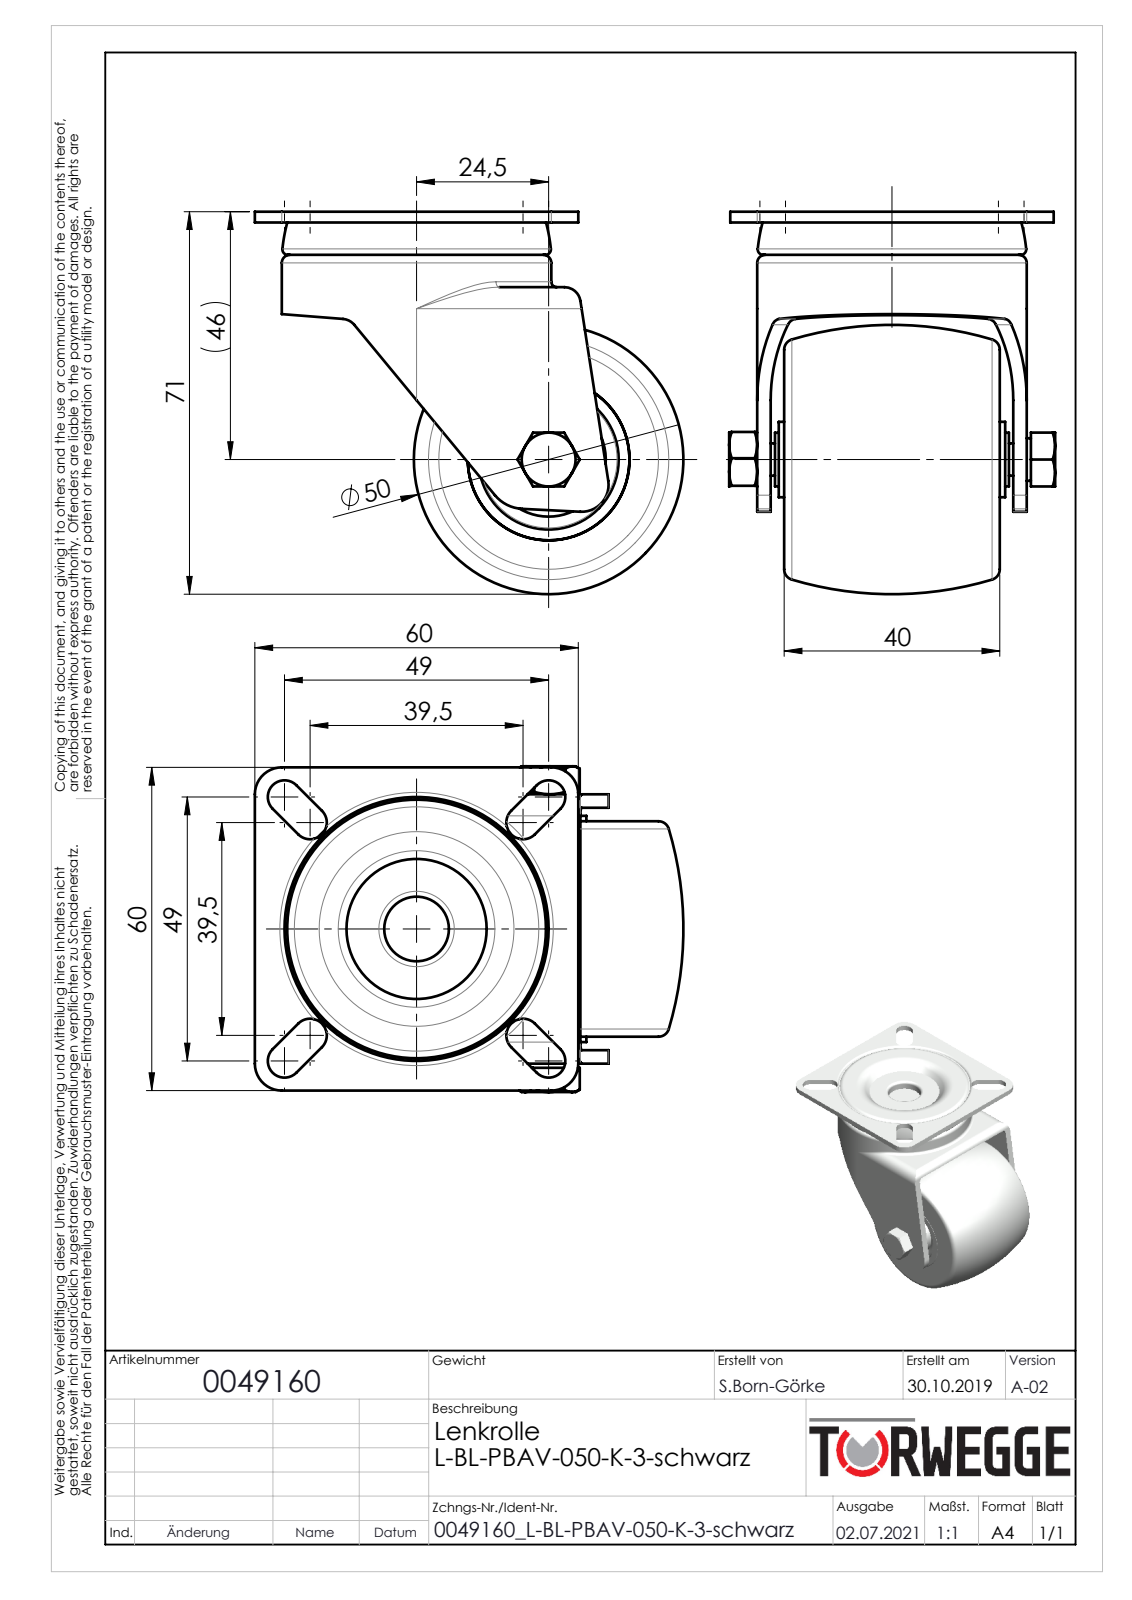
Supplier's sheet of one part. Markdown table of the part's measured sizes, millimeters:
| quantity | value |
| --- | --- |
| part name | 0049160 |
| STEP written by | SolidWorks 2020 (AUTOMOTIVE_DESIGN) |
| units | millimeters |
| bodies | 15 solids, 387 faces (95 planar, 109 cylindrical, 183 other) |
| overall size | 79.5 × 71 × 60.47 |
| volume | 96 286 mm³ |
| surface area | 52 229 mm² |
| round holes (diameter × count) | 5 × 1, 6 × 1, 6.1 × 1, 8 × 1, 10 × 1, 12 × 1, 14.5 × 1, 20 × 1, 21.2 × 1, 26 × 1, 30 × 1, 45 × 1 |
| round bosses / shafts (diameter × count) | 50 × 1, 21.5 × 1, 14.8 × 1, 14 × 1, 9.95 × 1, 7.9 × 1 |
| partial cylindrical surfaces (radius × count) | 3.1 × 8, 5 × 5, 1.5 × 2, 3 × 2, 4 × 2, 7 × 1 |
| main face-to-face distances | 2.5, 45, 8, 5, 10.5, 6, 42.5, 47.5, 8.5, 32 |
